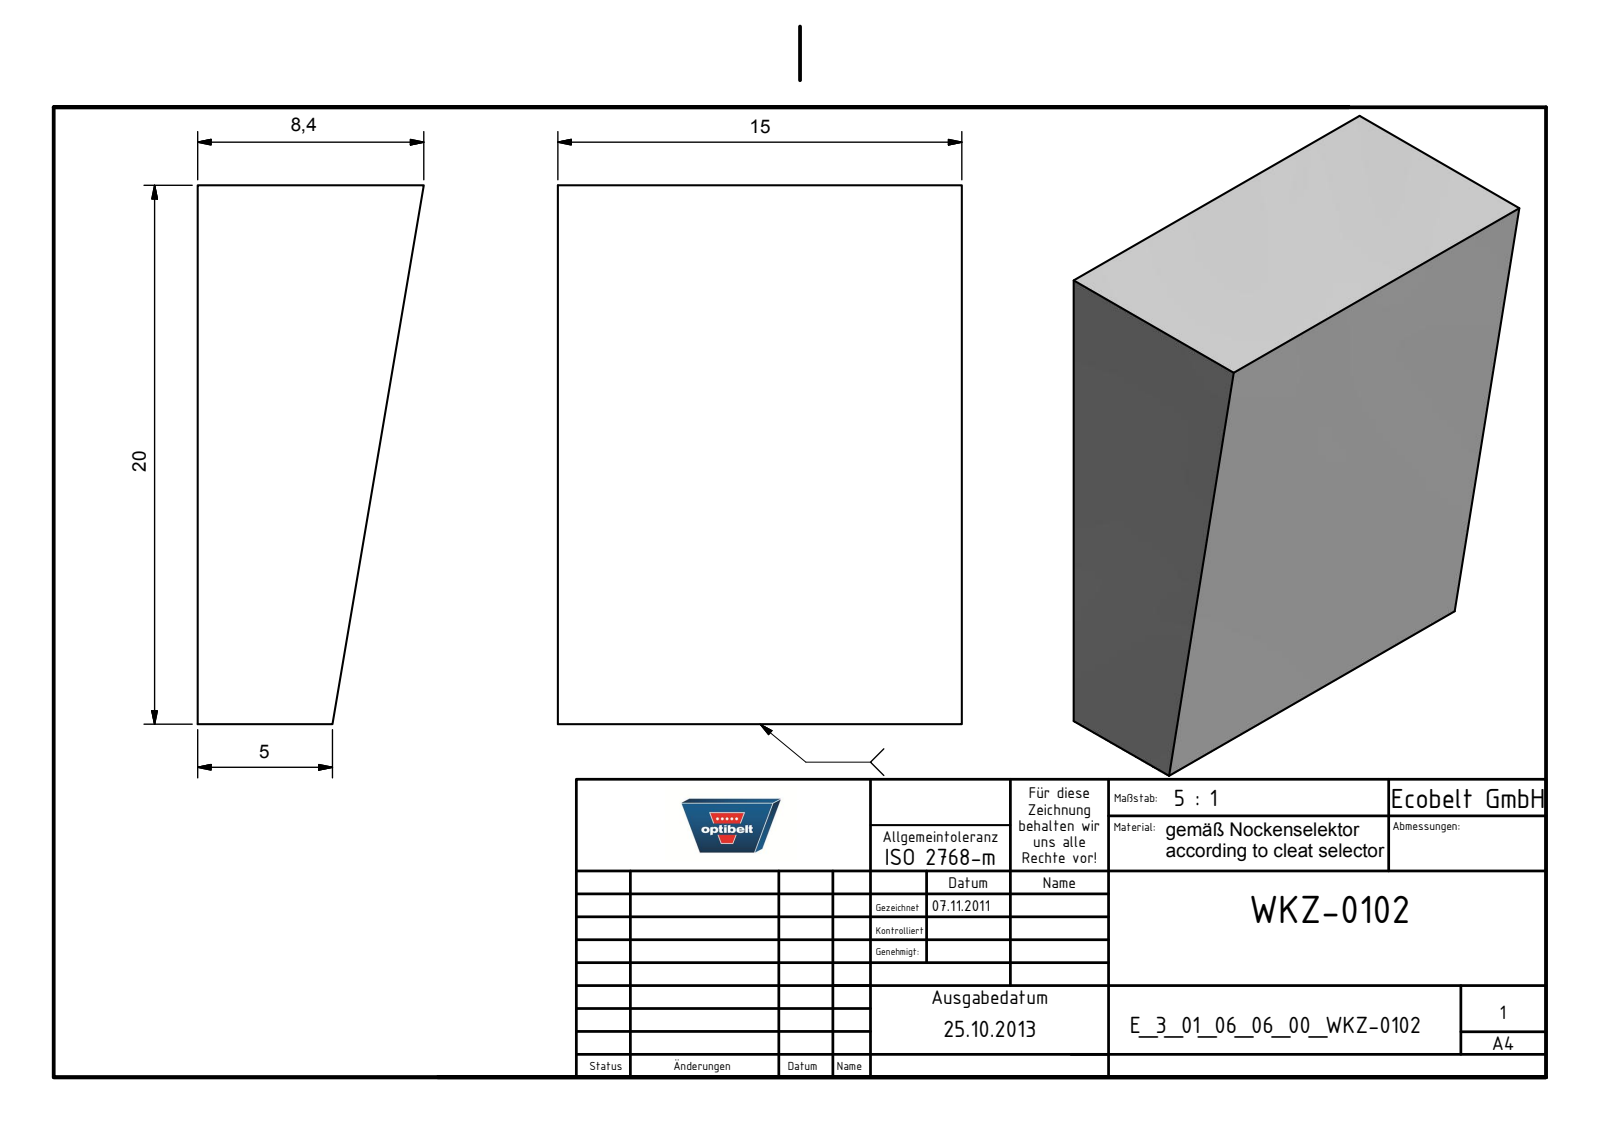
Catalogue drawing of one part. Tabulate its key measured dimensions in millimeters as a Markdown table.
| quantity | value |
| --- | --- |
| part name | E_3_01_06_06_00_WKZ-0102 |
| STEP written by | Autodesk Inventor 2025 (AUTOMOTIVE_DESIGN) |
| units | millimeters |
| bodies | 1 solid, 6 faces (6 planar, 0 cylindrical, 0 other) |
| overall size | 20 × 15 × 8.4 |
| volume | 2 010 mm³ |
| surface area | 1 073 mm² |
| main face-to-face distances | 15, 20 |
